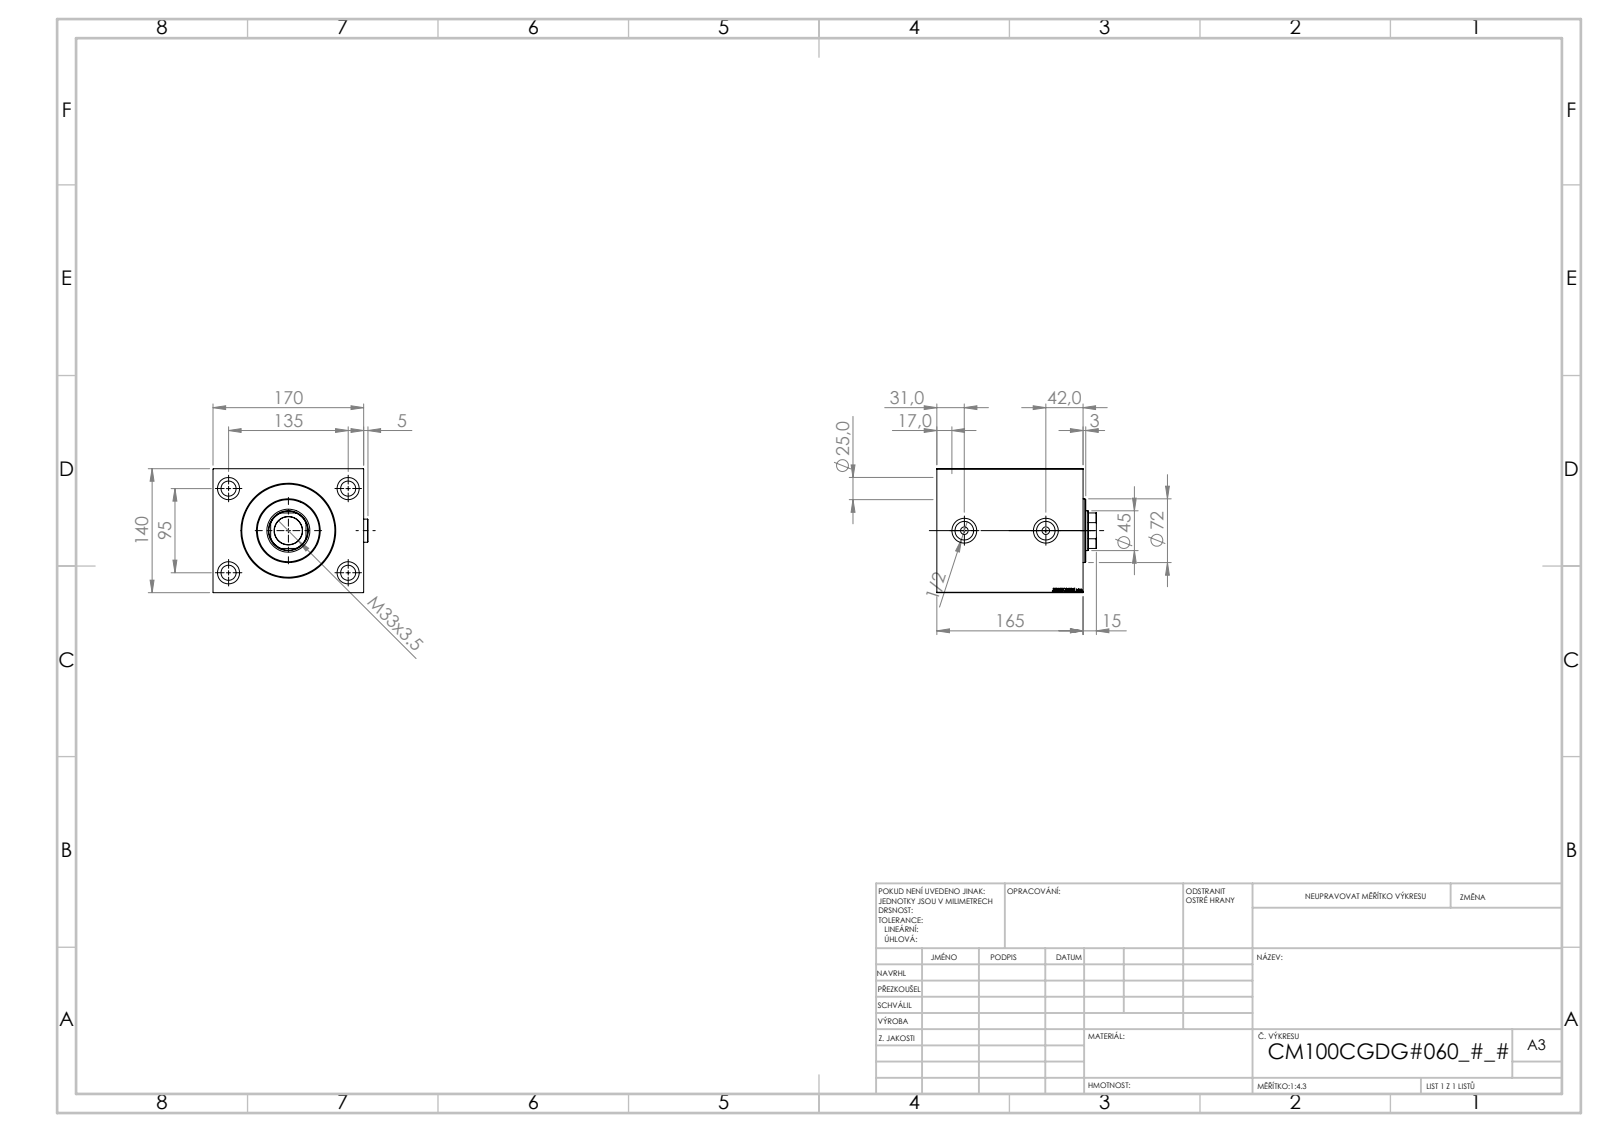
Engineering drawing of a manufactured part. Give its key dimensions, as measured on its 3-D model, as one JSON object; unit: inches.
{"part_name": "V450CM_C_Body; V450CM_C_VCP; V450CM_VC_B; Zatka_OIL_PORT", "step_written_by": "SolidWorks 2019 (CONFIG_CONTROL_DESIGN)", "units": "inches", "bodies": {"solids": 5, "faces": 919, "planar": 443, "cylindrical": 78, "other": 398}, "overall_size": [7.087, 6.886, 5.512], "volume_in3": 204.1, "surface_area_in2": 485.4, "round_holes": [[0.669, 4], [0.984, 4], [0.335, 2], [0.825, 2], [1.102, 2], [1.24, 1], [1.772, 1], [1.909, 1], [3.937, 1], [4.016, 1], [4.134, 1]], "round_bosses_or_shafts": [[1.024, 2], [2.835, 1]], "partial_cylinders_radius": [[0.866, 1]], "face_to_face_distances": [5.512, 6.693, 6.496, 5.472, 1.024, 0.591, 3.543, 4.882, 5.906, 2.362], "hole_center_spacings": [3.25, 3.74, 5.315, 6.499, 3.622]}
